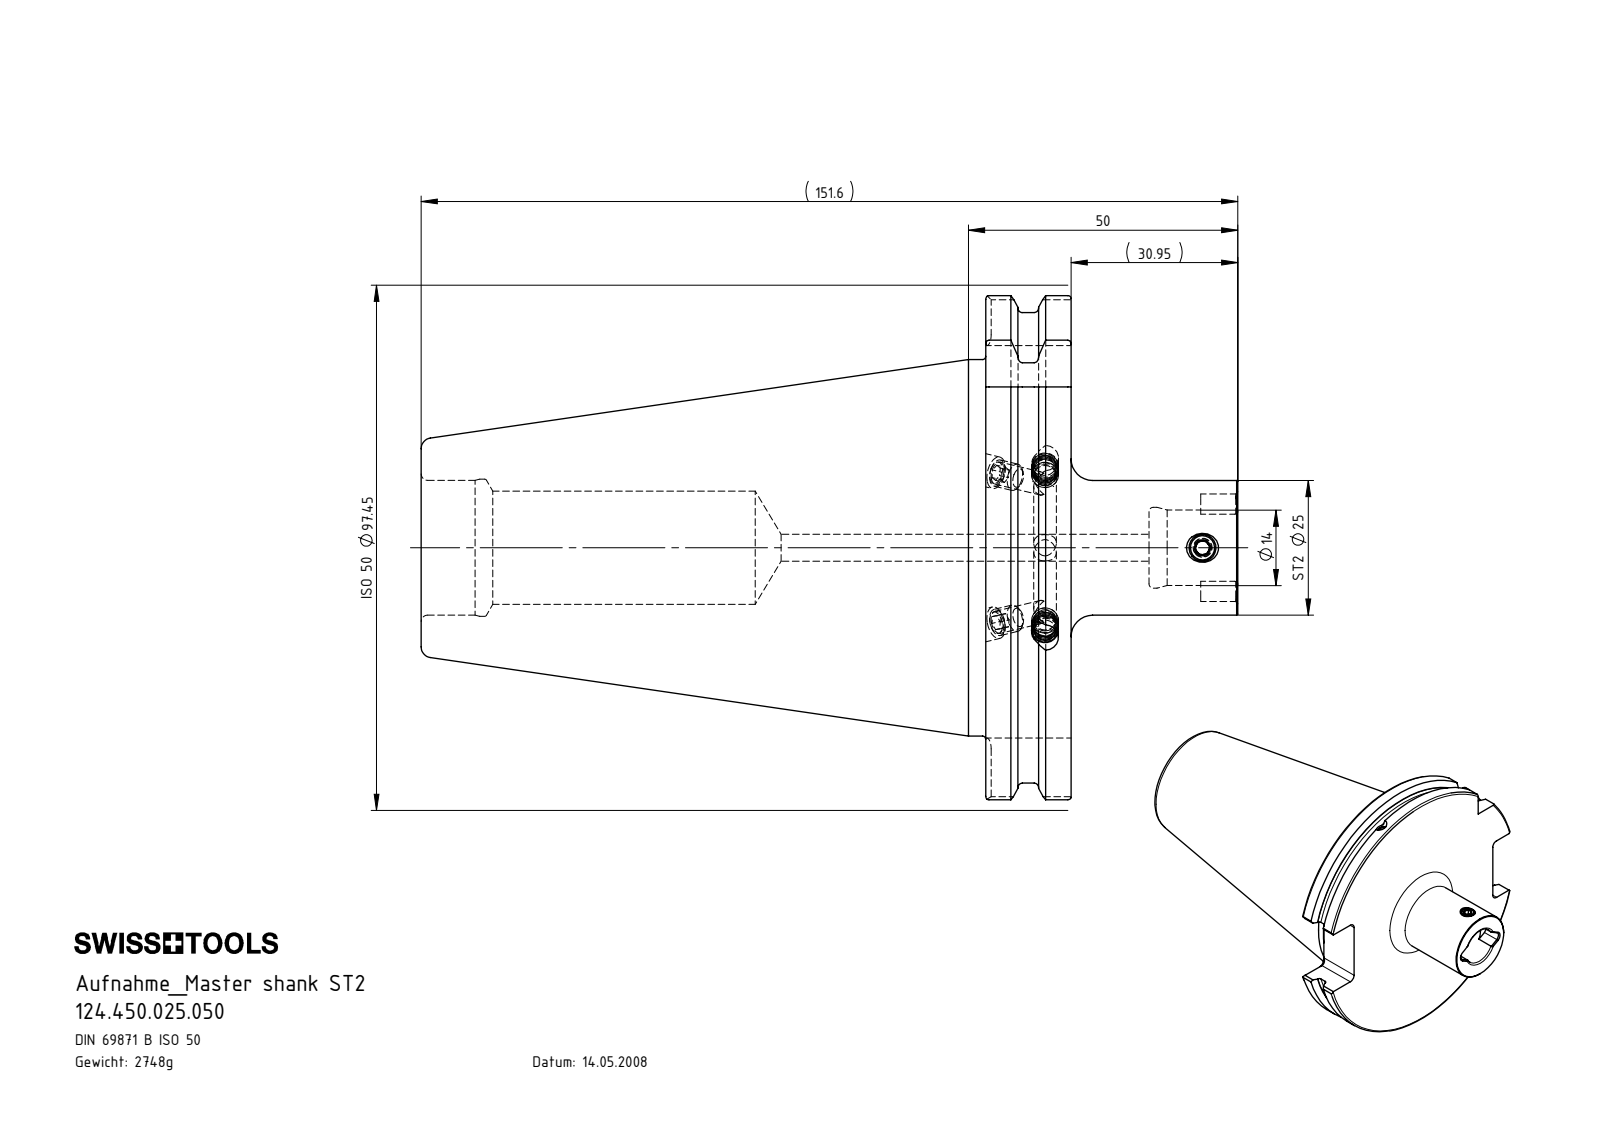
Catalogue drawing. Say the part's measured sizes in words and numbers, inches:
The part is named "ISO 4026 - M5 x 5_PreviewCfg; ST2-ER1.001.006_A; KVT_MB_600_050; SB5.ST2.K01.050 (+1 more)". Its 3-D file was written by "SolidWorks 2017 (AUTOMOTIVE_DESIGN)". It is 8 solids with 206 faces: 78 planar, 46 cylindrical and 82 other. Overall it measures 5.969 by 3.837 by 3.681 inches. Its volume is 21.36 cubic inches and its surface area 71.49 square inches. Round holes: 3 of diameter 0.165, 2 of diameter 0.157, 2 of diameter 0.197, 2 of diameter 0.236, 1 of diameter 0.098, 1 of diameter 0.177, 1 of diameter 0.551, 1 of diameter 0.591, 1 of diameter 0.827, 1 of diameter 0.984, 1 of diameter 1.002. Round bosses or shafts: 4 of diameter 0.197, 1 of diameter 3.583, 1 of diameter 2.75. Partial cylindrical surfaces (rounded edges, fillets, slot ends): 8 of radius 0.079, 2 of radius 0.071, 1 of radius 1.919. The main face-to-face distances are 0.624, 4.126, 4.75, 2.866, 5.969, 1.843, 1.219, 1.012, 5.319, 1.193.
